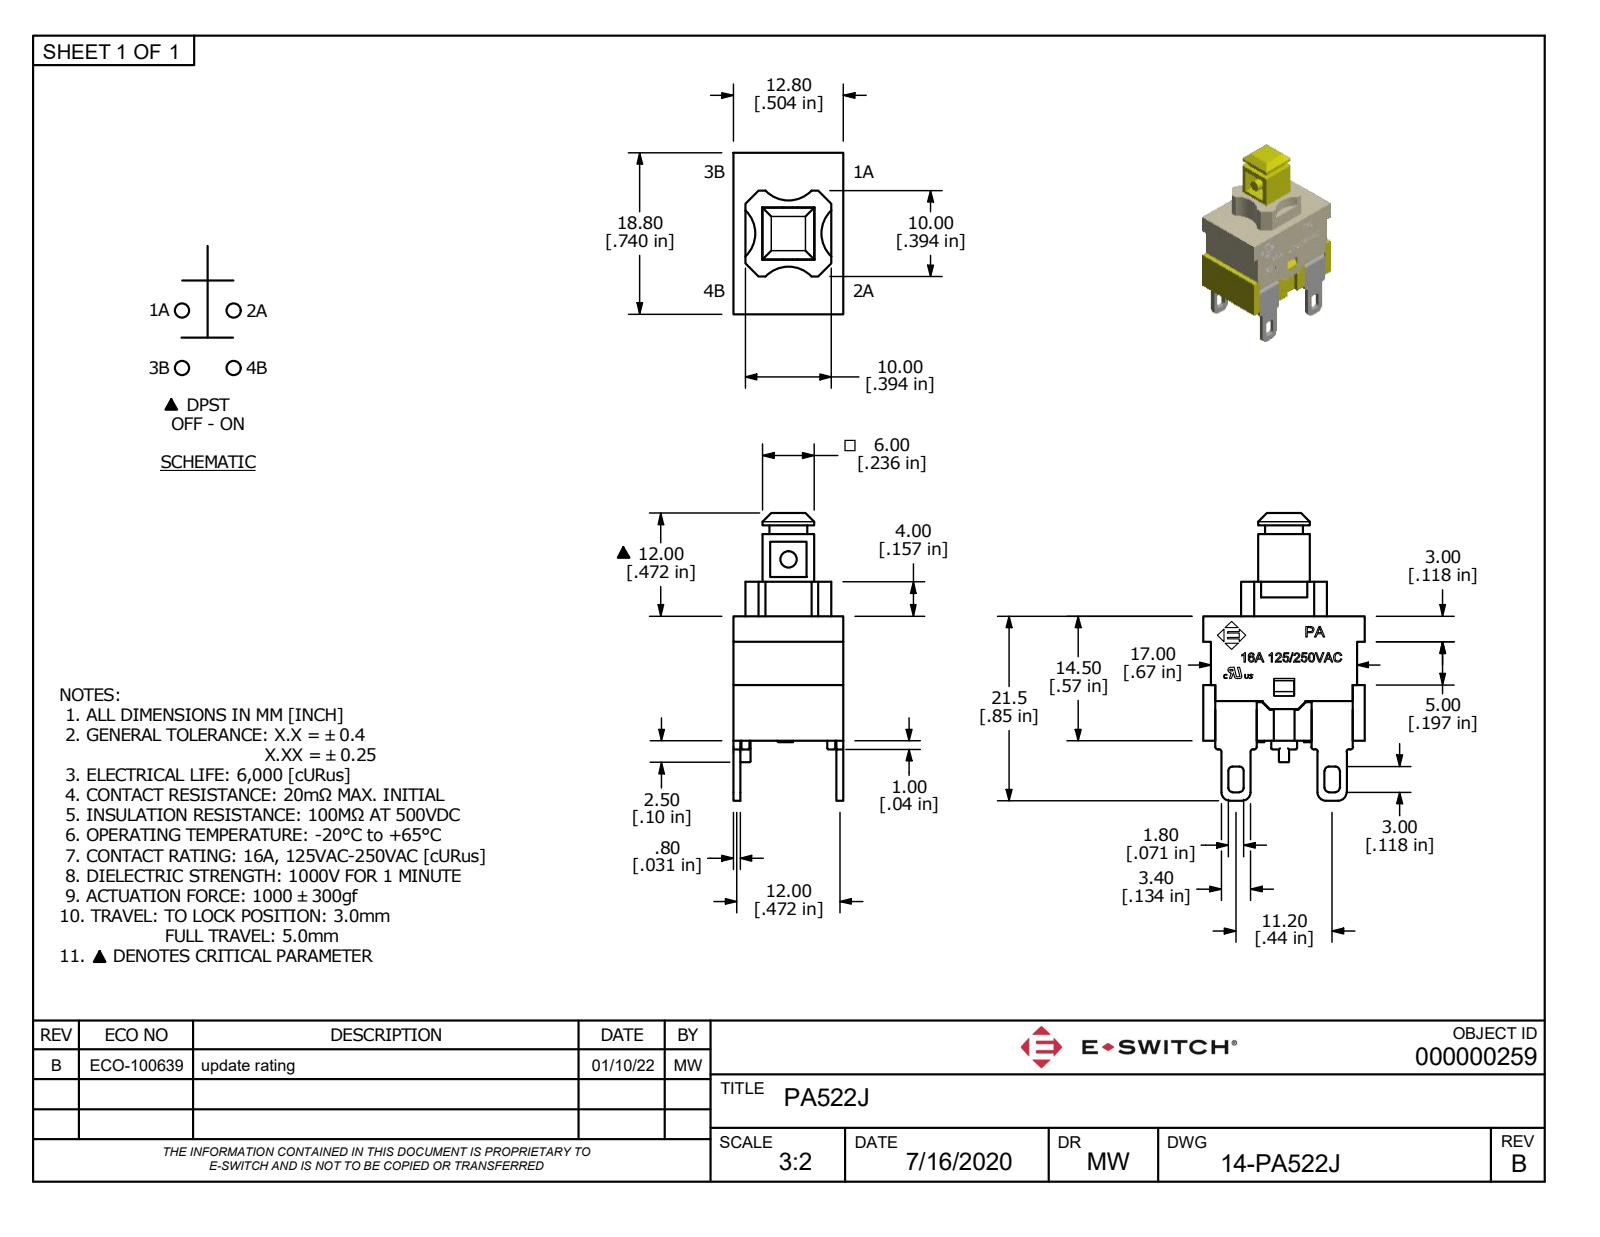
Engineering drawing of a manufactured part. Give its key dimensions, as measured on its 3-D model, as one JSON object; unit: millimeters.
{"part_name": "PA522J", "step_written_by": "Autodesk Inventor 2022 (AUTOMOTIVE_DESIGN)", "units": "millimeters", "bodies": {"solids": 1, "faces": 883, "planar": 634, "cylindrical": 118, "other": 131}, "overall_size": [33.5, 18.8, 12.8], "volume_mm3": 2230, "surface_area_mm2": 4470, "round_holes": [[3, 1]], "round_bosses_or_shafts": [[0.95, 4], [2.5, 2], [1.9, 1]], "partial_cylinders_radius": [[0.25, 24], [0.12, 16], [0.5, 9], [0.15, 8], [0.3, 8], [1, 8], [3.71, 4], [1.72, 1]], "face_to_face_distances": [0.8, 12, 0.9, 16.8, 12.8, 2, 1, 8.6, 4.4, 1.1]}
